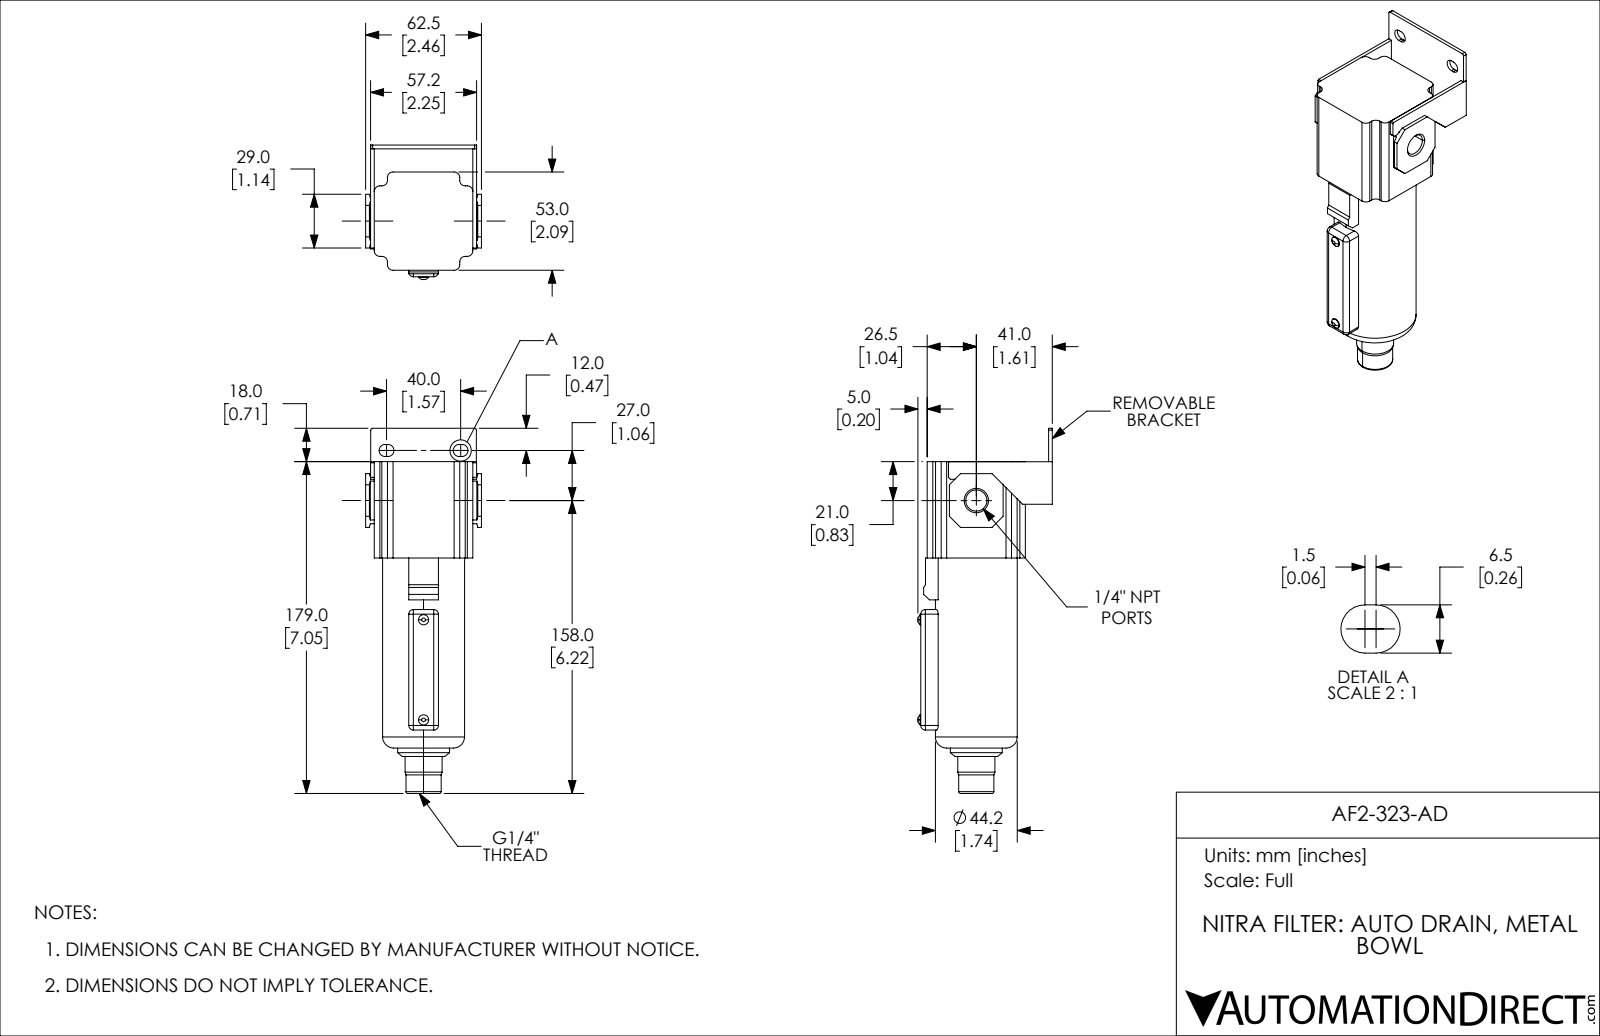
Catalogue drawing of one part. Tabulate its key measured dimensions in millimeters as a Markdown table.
| quantity | value |
| --- | --- |
| part name | AF2-323-AD |
| STEP written by | SolidWorks 2019 (CONFIG_CONTROL_DESIGN) |
| units | millimeters |
| bodies | 1 solid, 161 faces (95 planar, 44 cylindrical, 22 other) |
| overall size | 197 × 72.5 × 62.5 |
| volume | 321 429 mm³ |
| surface area | 42 034 mm² |
| round holes (diameter × count) | 8.57 × 1, 11.45 × 1 |
| round bosses / shafts (diameter × count) | 5.5 × 2, 44.2 × 1, 28 × 1, 20 × 1, 19 × 1 |
| partial cylindrical surfaces (radius × count) | 3 × 12, 2.5 × 8, 3.25 × 4, 1 × 2 |
| main face-to-face distances | 2, 12.5, 14.5, 67.5, 65.5, 53, 55.2, 2.65, 4.65, 57.85 |
